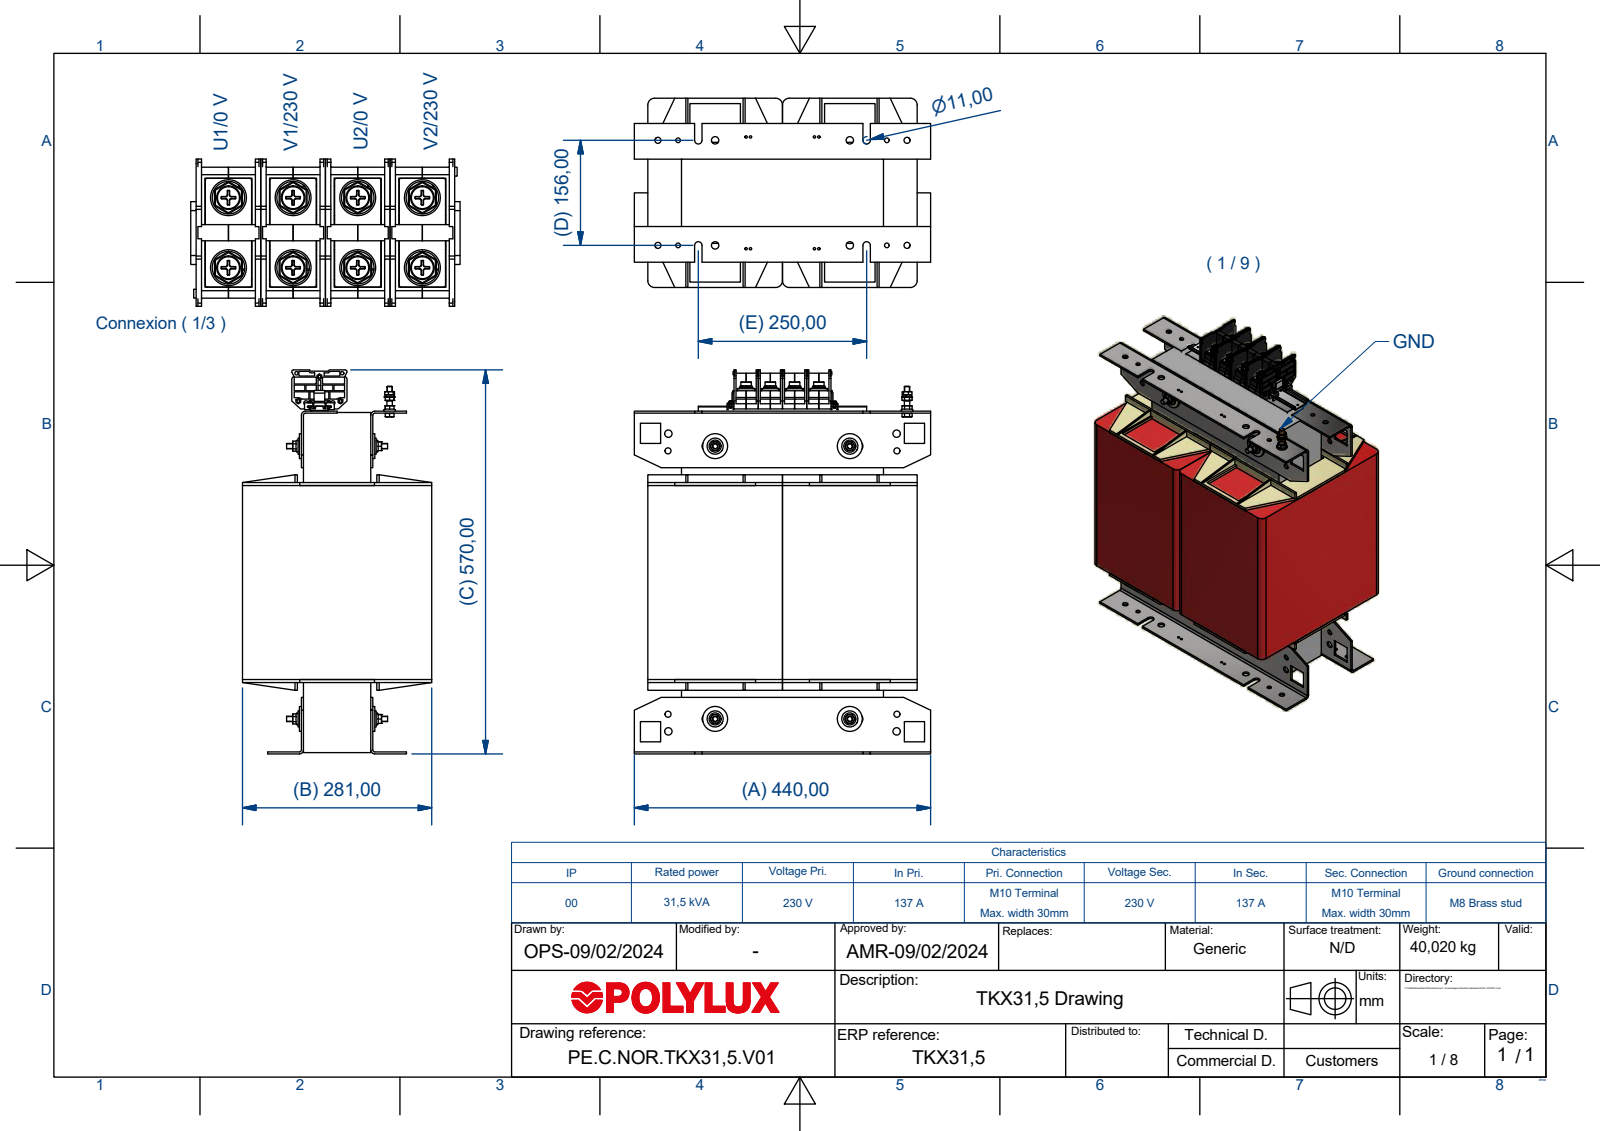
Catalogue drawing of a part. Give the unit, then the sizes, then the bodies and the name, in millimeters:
Units: millimetres
Overall size (bounding box): 570.25 × 440 × 281
Round holes (diameter × count): ⌀3.5 ×12, ⌀9 ×10, ⌀11 ×10, ⌀8.3 ×8, ⌀10.5 ×8, ⌀10.7 ×8, ⌀12.25 ×8, ⌀14 ×8, ⌀7 ×6, ⌀6.65 ×5, ⌀8.4 ×5, ⌀13 ×4
Round bosses / shafts (diameter × count): ⌀20 ×8, ⌀18.1 ×8, ⌀9.85 ×8, ⌀8 ×5, ⌀37 ×4, ⌀24 ×4, ⌀3.92 ×4, ⌀3 ×4
Partial cylindrical surfaces — rounded edges, fillets, slot ends (radius × count): R0.5 ×74, R1 ×70, R0.25 ×12, R0.93 ×8, R10 ×8, R5.5 ×6, R1.6 ×4, R2 ×4
Main face-to-face distances: 200, 4, 100, 196, 104, 150, 50, 3, 46, 154
Hole centre spacings: 103, 340, 6.58, 30, 46.27, 52.82, 53, 55
Volume: 40 020 000 mm³ · Surface area: 3 010 000 mm²
Bodies: 82 solids, 4222 faces (3062 planar, 749 cylindrical, 411 other)
Part name (STEP PRODUCT): TKX31.5
STEP written by: Autodesk Inventor 2018 (AUTOMOTIVE_DESIGN)
